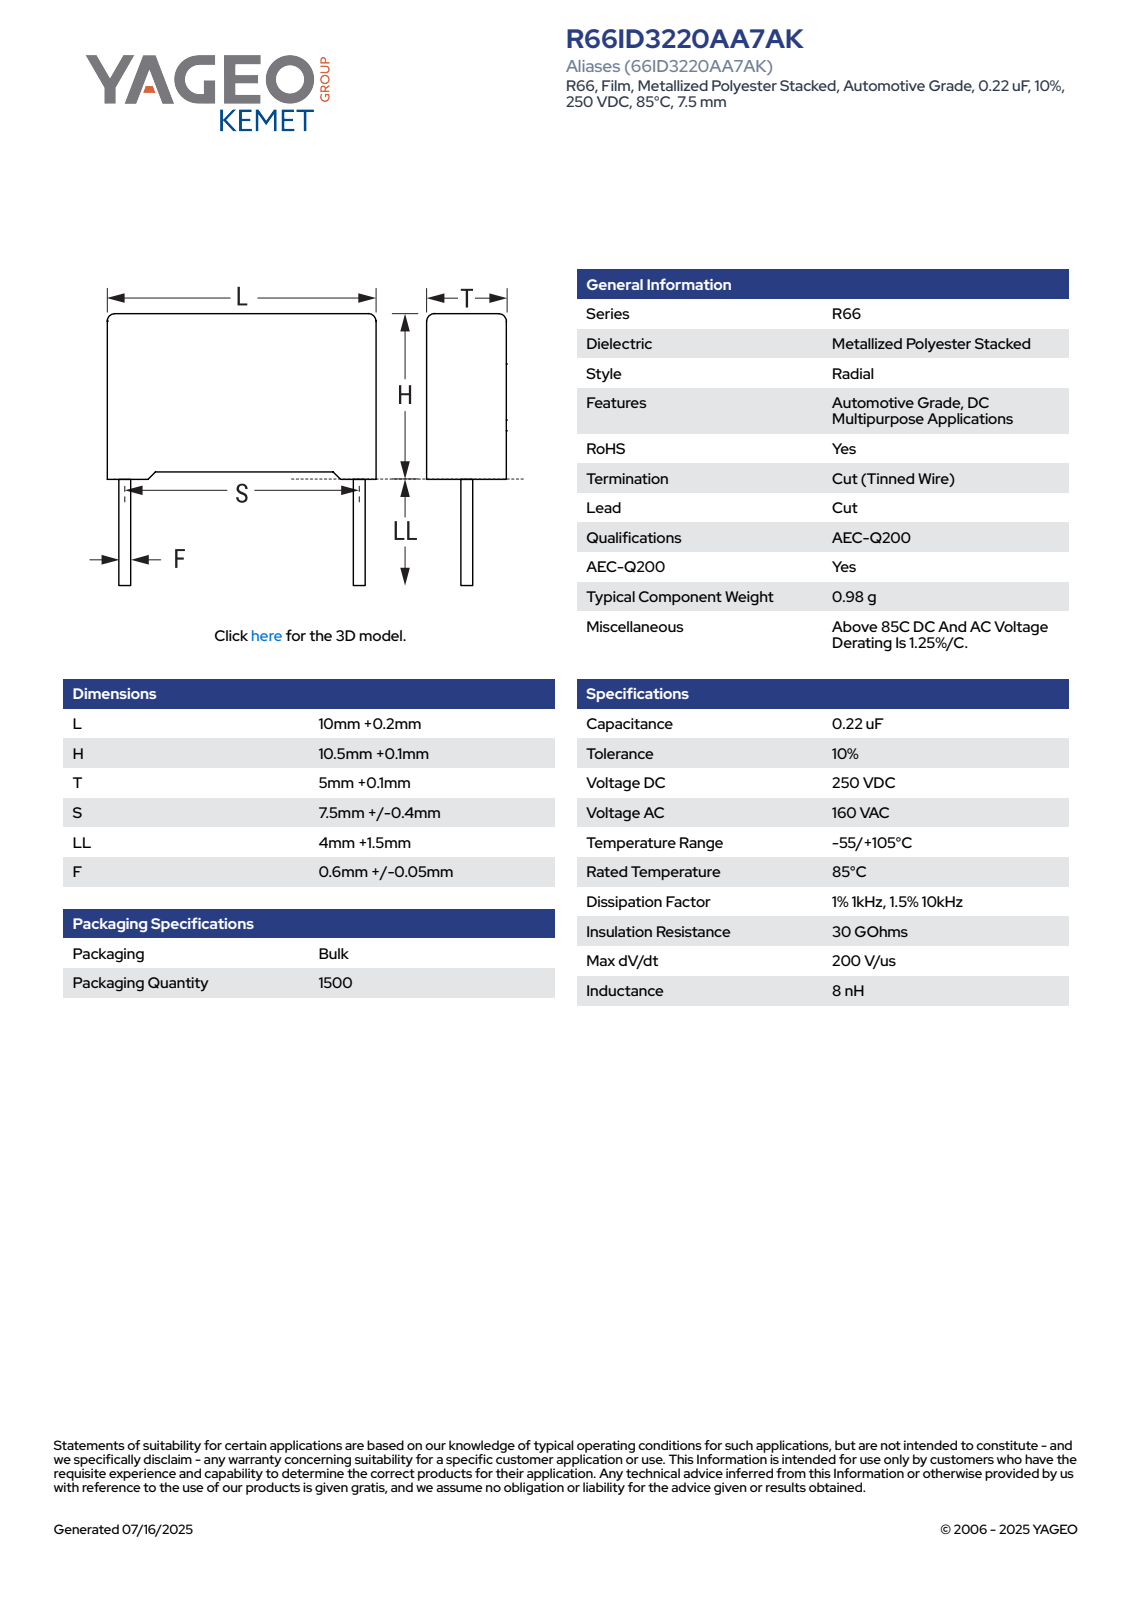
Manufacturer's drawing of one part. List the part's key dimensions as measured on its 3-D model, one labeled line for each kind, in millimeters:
Part name (STEP PRODUCT): CFR_RB2_10X10.5X5_L10.2H10.6T5.1S7.5LL5.5F0.65
STEP written by: SolidWorks 2021 (AUTOMOTIVE_DESIGN)
Units: millimetres
Bodies: 4 solids, 85 faces (77 planar, 8 cylindrical, 0 other)
Overall size (bounding box): 16.1 × 10.2 × 5.11
Volume: 521 mm³ · Surface area: 470 mm²
Round bosses / shafts (diameter × count): ⌀0.65 ×2
Partial cylindrical surfaces — rounded edges, fillets, slot ends (radius × count): R0.5 ×4
Main face-to-face distances: 5.1, 10.2, 9.85, 0.34, 4.76, 0.75, 10.6, 9.86, 4.42, 9.52
